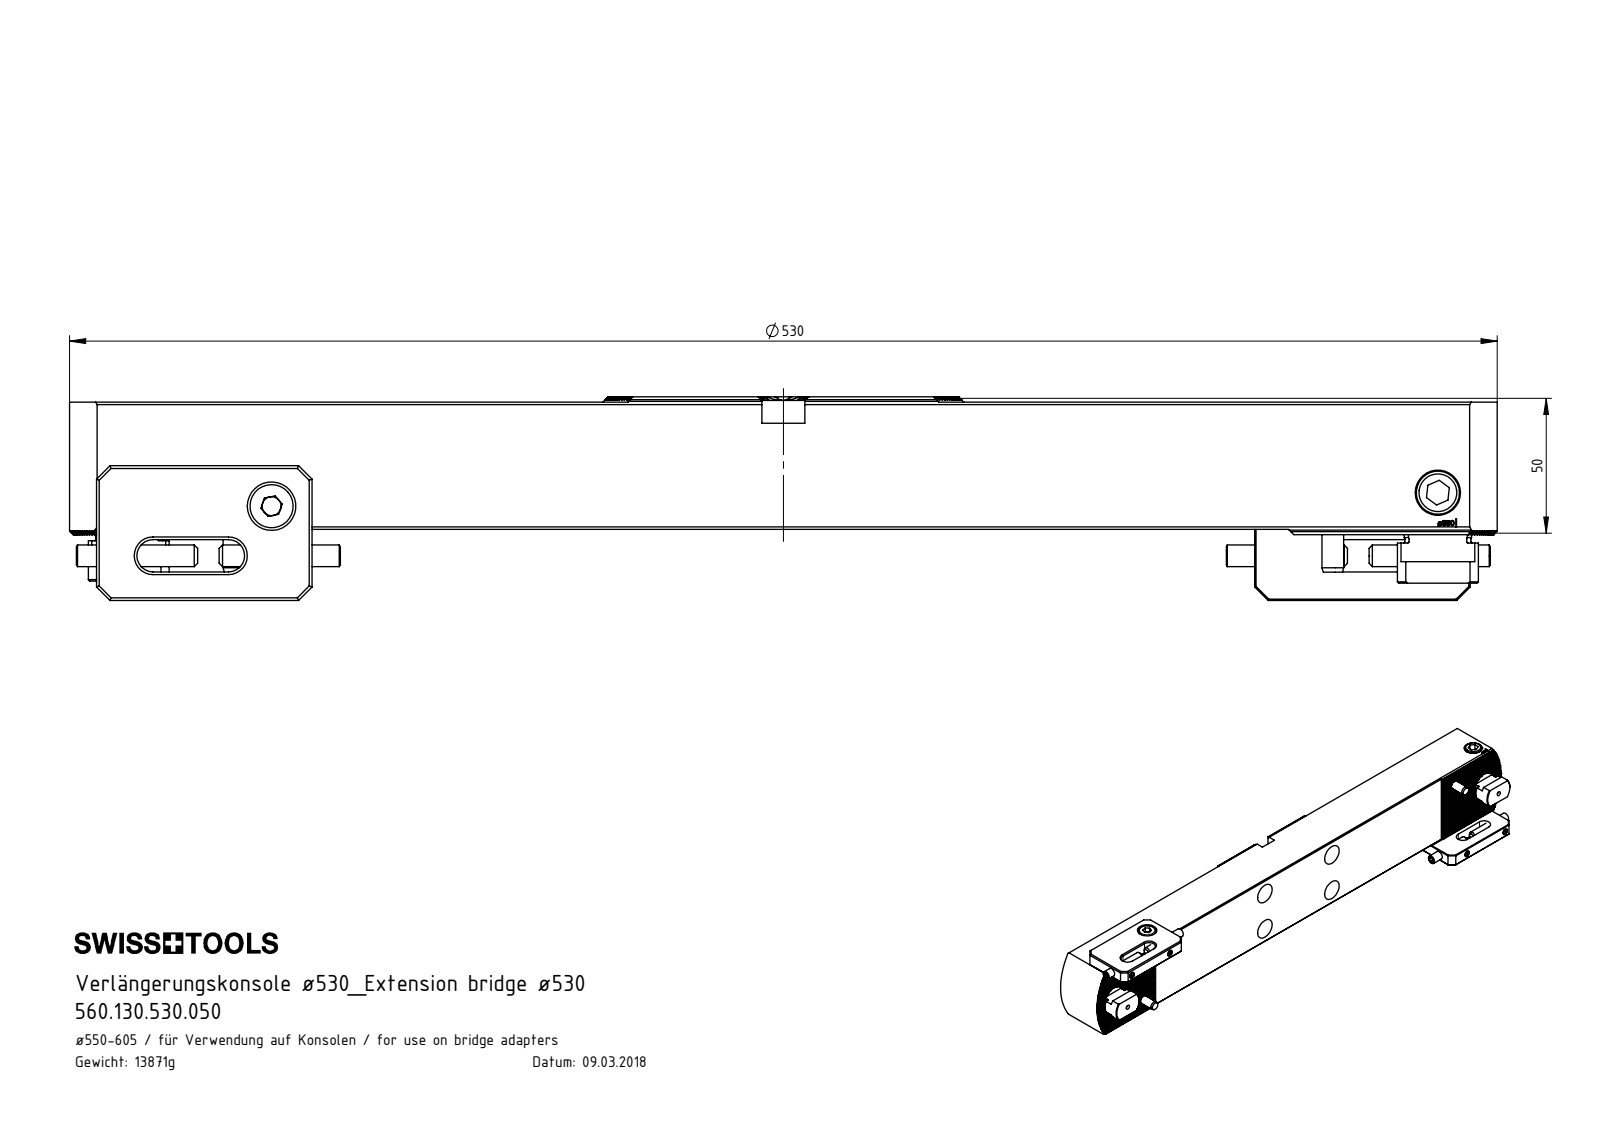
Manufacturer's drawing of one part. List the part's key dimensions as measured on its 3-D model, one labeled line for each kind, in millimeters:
Part name (STEP PRODUCT): Ko1-VK1.530.050_E; VK1-ER3.001.028_A; VK1-ER7.001.012_mit langer Schraube; ISO 4766 - M6x12_ISO 4766 - M6 x 10 (+8 more)
STEP written by: SolidWorks 2017 (CONFIG_CONTROL_DESIGN)
Units: millimetres
Bodies: 27 solids, 1575 faces (874 planar, 402 cylindrical, 299 other)
Overall size (bounding box): 530 × 94 × 75.58
Volume: 1 773 000 mm³ · Surface area: 214 241 mm²
Round holes (diameter × count): ⌀5 ×4, ⌀6 ×4, ⌀6.8 ×4, ⌀13 ×4, ⌀19 ×4, ⌀2 ×2, ⌀8 ×2, ⌀8.5 ×2, ⌀10.5 ×2, ⌀11 ×2, ⌀14 ×2, ⌀18 ×2
Round bosses / shafts (diameter × count): ⌀16 ×4, ⌀6 ×4, ⌀10 ×2, ⌀8 ×2
Partial cylindrical surfaces — rounded edges, fillets, slot ends (radius × count): R0.14 ×66, R2 ×8, R6 ×4, R12.3 ×2, R15 ×2, R65 ×2, R7.95 ×1
Main face-to-face distances: 47.16, 70, 12, 82, 1.73, 8.66, 3.46, 6.93, 0.5, 41.57
Hole centre spacings: 486, 200, 287.7, 7.9, 18.55, 19.61, 34.53, 35.09
